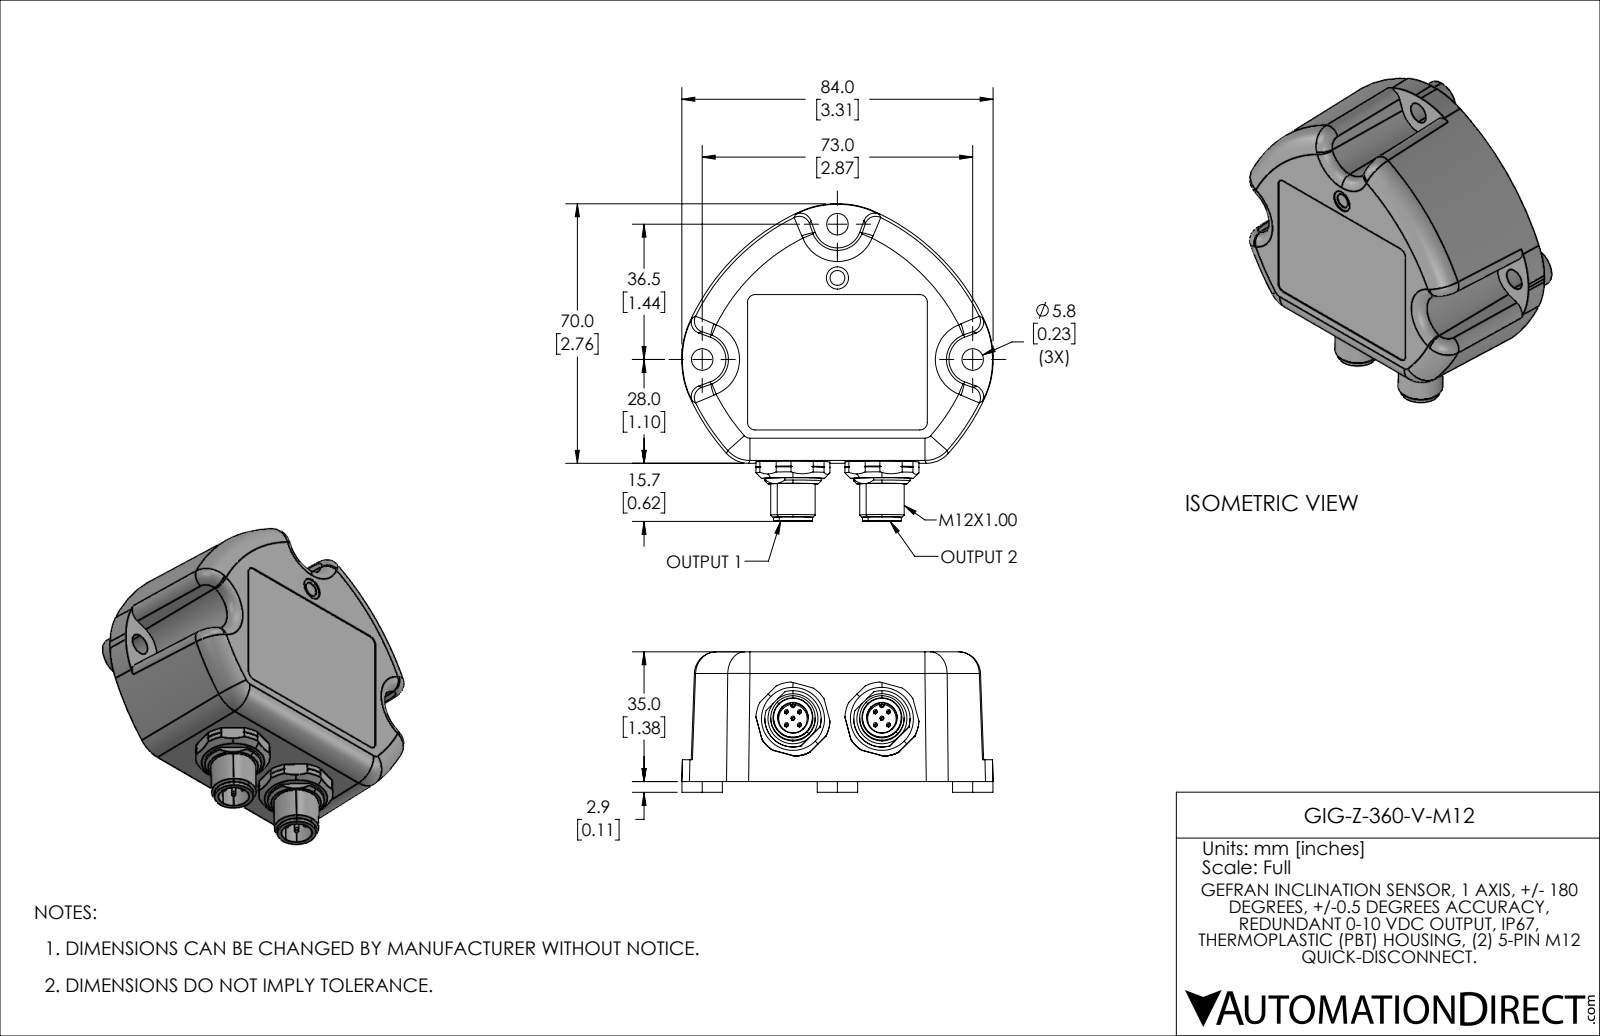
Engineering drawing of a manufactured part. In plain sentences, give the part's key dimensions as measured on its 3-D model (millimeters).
The part is named "GIG-Z-360-V-M12". Its 3-D file was written by "SolidWorks 2021 (AUTOMOTIVE_DESIGN)". It is 1 solid with 365 faces: 87 planar, 123 cylindrical and 155 other. Overall it measures 85.7 by 84 by 37.9 millimeters. Its volume is 148 000 cubic millimeters and its surface area 20 890 square millimeters. Round holes: 3 of diameter 5.8, 2 of diameter 8.3, 1 of diameter 4, 1 of diameter 6. Round bosses or shafts: 10 of diameter 1, 3 of diameter 10.9, 2 of diameter 12, 2 of diameter 10.5. Partial cylindrical surfaces (rounded edges, fillets, slot ends): 4 of radius 0.5, 4 of radius 2, 3 of radius 7.6, 2 of radius 0.6, 2 of radius 6.9, 2 of radius 10, 1 of radius 6, 1 of radius 7.6. The main face-to-face distances are 34.8, 35, 5.9, 28.9, 29.1, 2.9, 8.8, 37.7, 37.9, 17. The hole center spacings are 42.6, 51.6, 14.5, 24, 73.
